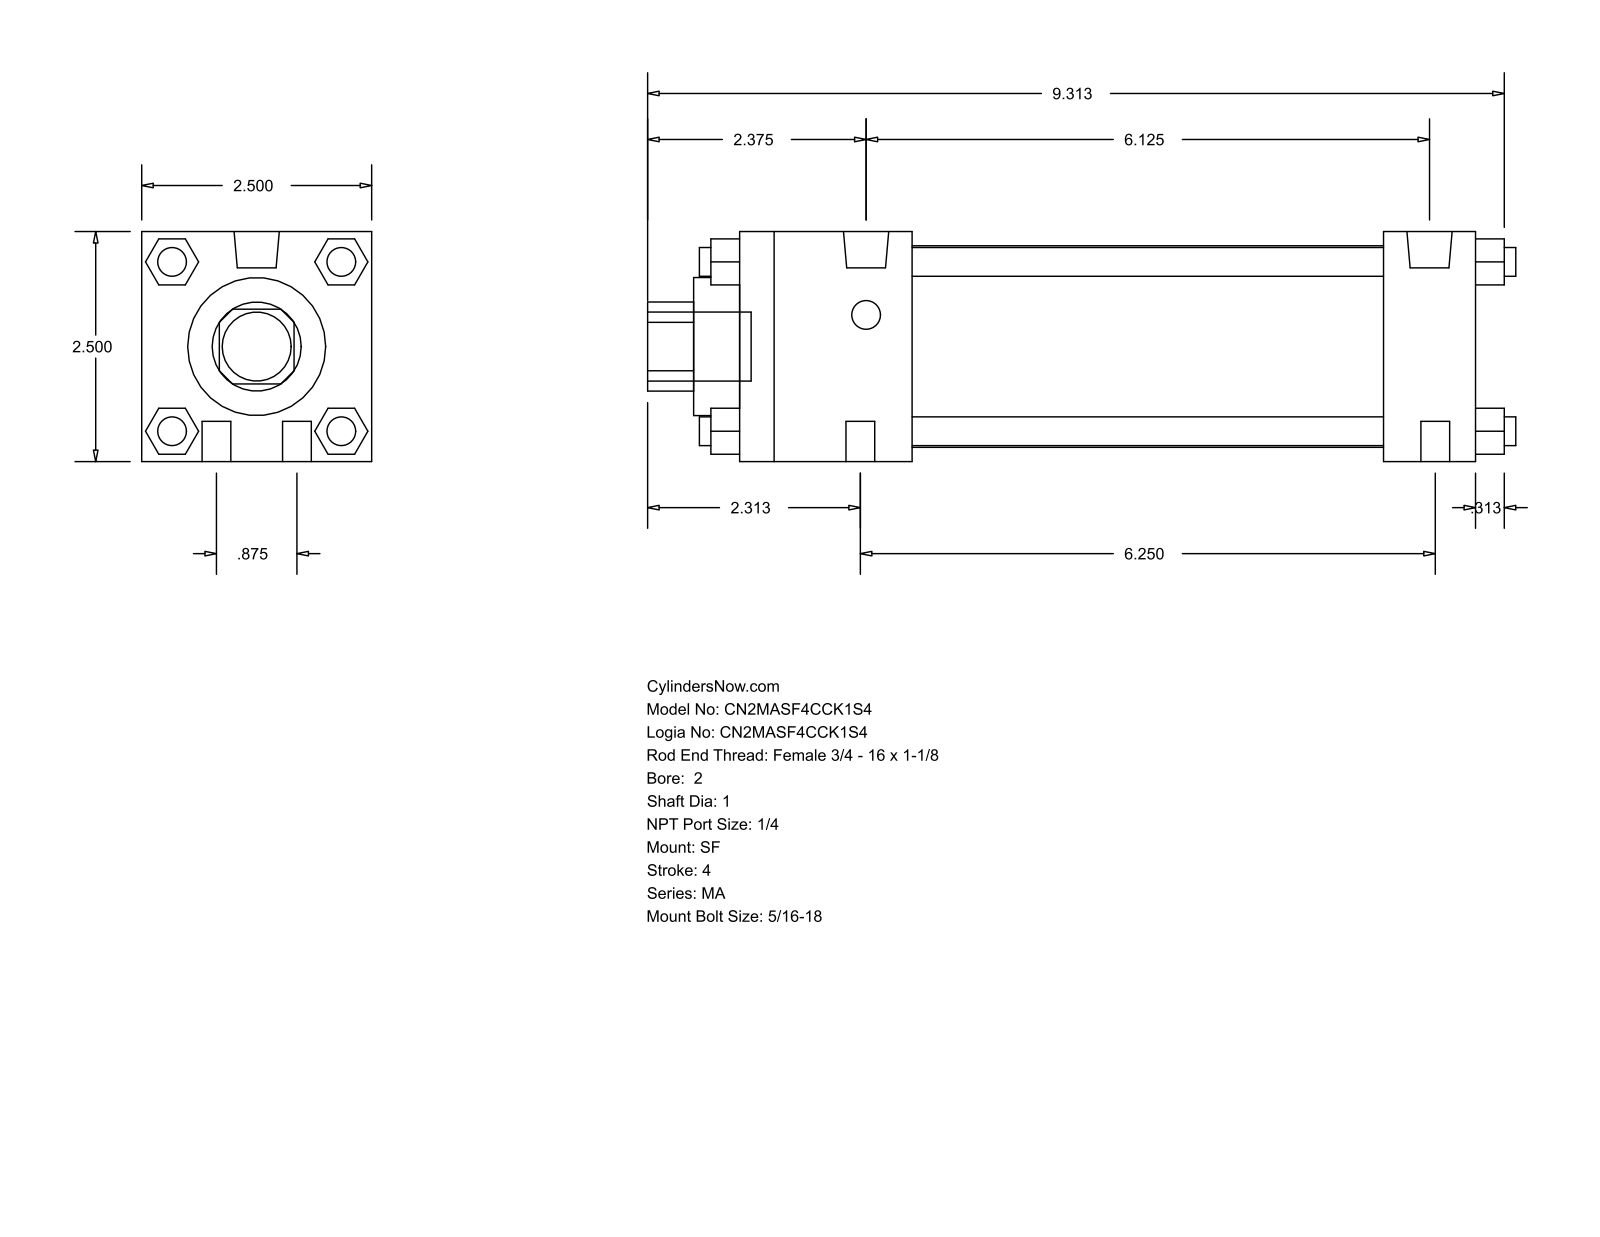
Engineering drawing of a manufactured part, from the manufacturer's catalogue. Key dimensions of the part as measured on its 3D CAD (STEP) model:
Part name (STEP PRODUCT): MA_SF__0200_1
STEP written by: GSSL Pune (CONFIG_CONTROL_DESIGN)
Units: millimetres
Bodies: 0 solids, 124 faces (94 planar, 30 cylindrical, 0 other)
Overall size (bounding box): 239.71 × 63.5 × 63.5
Round holes (diameter × count): ⌀25.4 ×1, ⌀38.1 ×1, ⌀55.63 ×1
Round bosses / shafts (diameter × count): ⌀7.94 ×10, ⌀12.49 ×2, ⌀19.05 ×1
Partial cylindrical surfaces — rounded edges, fillets, slot ends (radius × count): R12.29 ×1
Main face-to-face distances: 63.5, 203.2, 12.7, 25.4, 177.8, 47.63, 130.17, 155.57, 40.47, 23.37
